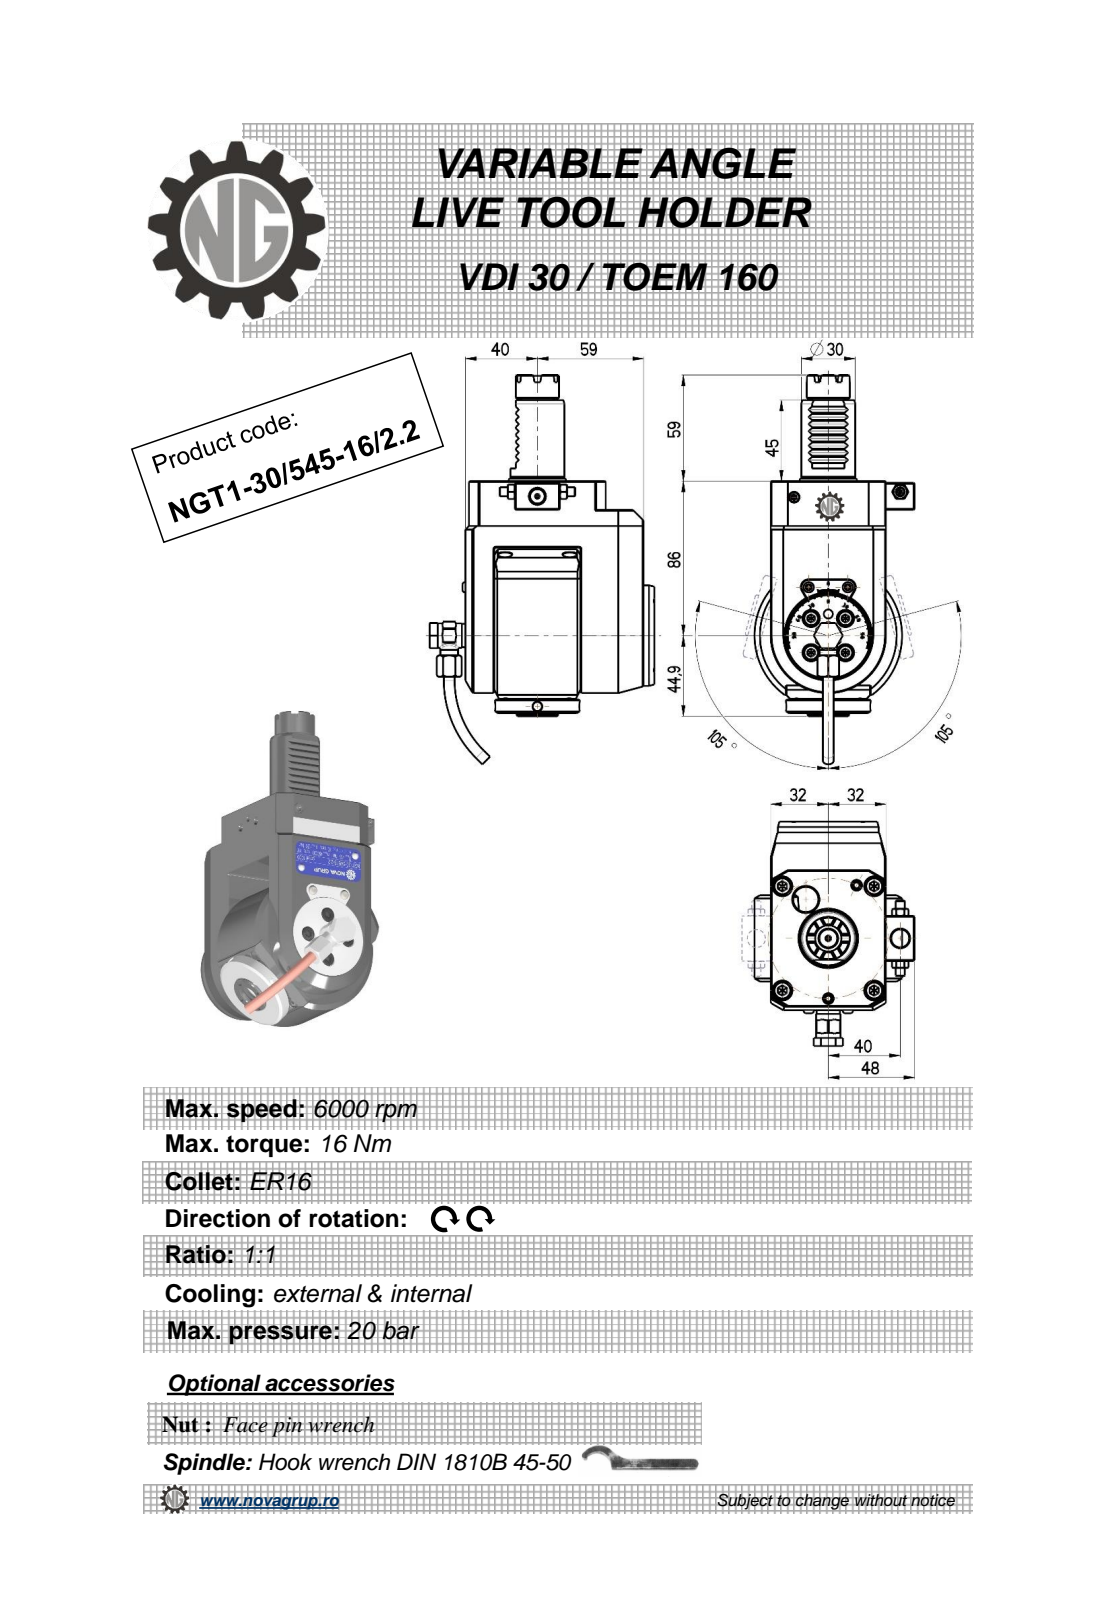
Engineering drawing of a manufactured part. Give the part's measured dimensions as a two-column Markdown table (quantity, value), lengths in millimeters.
| quantity | value |
| --- | --- |
| part name | NGT1_30_541_16_2_2 |
| STEP written by | PRO/ENGINEER BY PARAMETRIC TECHNOLOGY CORPORATION, 2010280 (CONFIG_CONTROL_DESIGN) |
| units | millimeters |
| bodies | 1 solid, 538 faces (235 planar, 140 cylindrical, 163 other) |
| overall size | 216.67 × 124.9 × 89 |
| volume | 774 226 mm³ |
| surface area | 71 517 mm² |
| round holes (diameter × count) | 3.2 × 4, 4 × 3, 5 × 2, 10 × 2, 3 × 1, 4.2 × 1, 6.2 × 1, 9 × 1, 9.5 × 1, 11 × 1, 12.5 × 1 |
| round bosses / shafts (diameter × count) | 6 × 2, 5.7 × 2, 56 × 1, 47 × 1, 35 × 1, 30 × 1, 24 × 1, 23 × 1 |
| partial cylindrical surfaces (radius × count) | 0.26 × 12, 0.3 × 8, 0.16 × 6, 0.5 × 4, 1 × 2, 7.6 × 1, 7.7 × 1, 32 × 1 |
| main face-to-face distances | 64, 16, 37, 99, 6, 105, 14, 62, 21, 83 |
| hole center spacings | 9.25, 13.08, 18.5, 41.06, 49.87, 50.26, 0.4, 30.75 |
